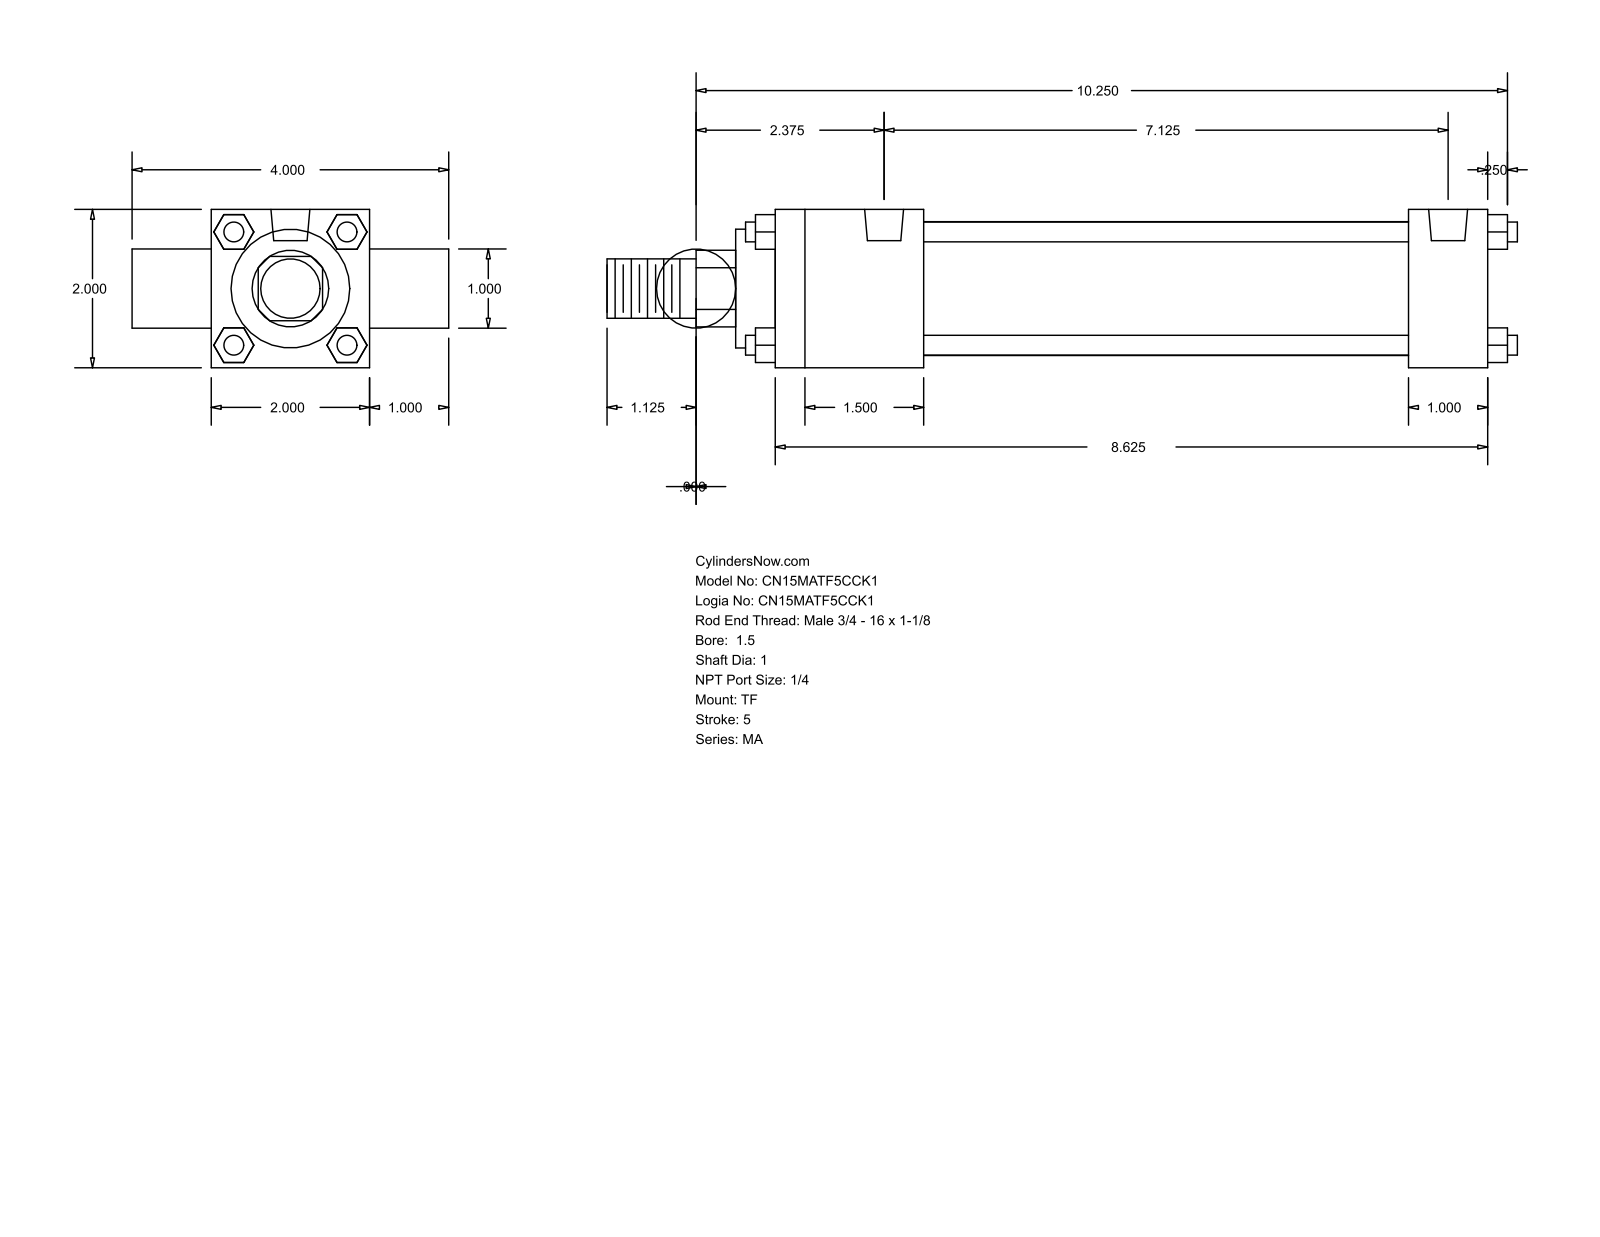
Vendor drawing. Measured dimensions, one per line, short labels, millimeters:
name: MA_TF__0150_1
written by: GSSL Pune (CONFIG_CONTROL_DESIGN)
unit: mm
bodies: 0 solids, 120 faces (92 planar, 28 cylindrical, 0 other)
size: 292.1 × 101.6 × 50.8
holes: 3× ⌀7.94, 2× ⌀12.49
bosses: 4× ⌀6.35, 2× ⌀25.4, 1× ⌀42.93, 1× ⌀38.1, 1× ⌀19.05
rounds: 1× R12.29
face distances: 50.8, 25.4, 228.6, 76.2, 6.35, 47.63, 203.2, 155.57, 180.97, 241.3
hole spacings: 180.97
